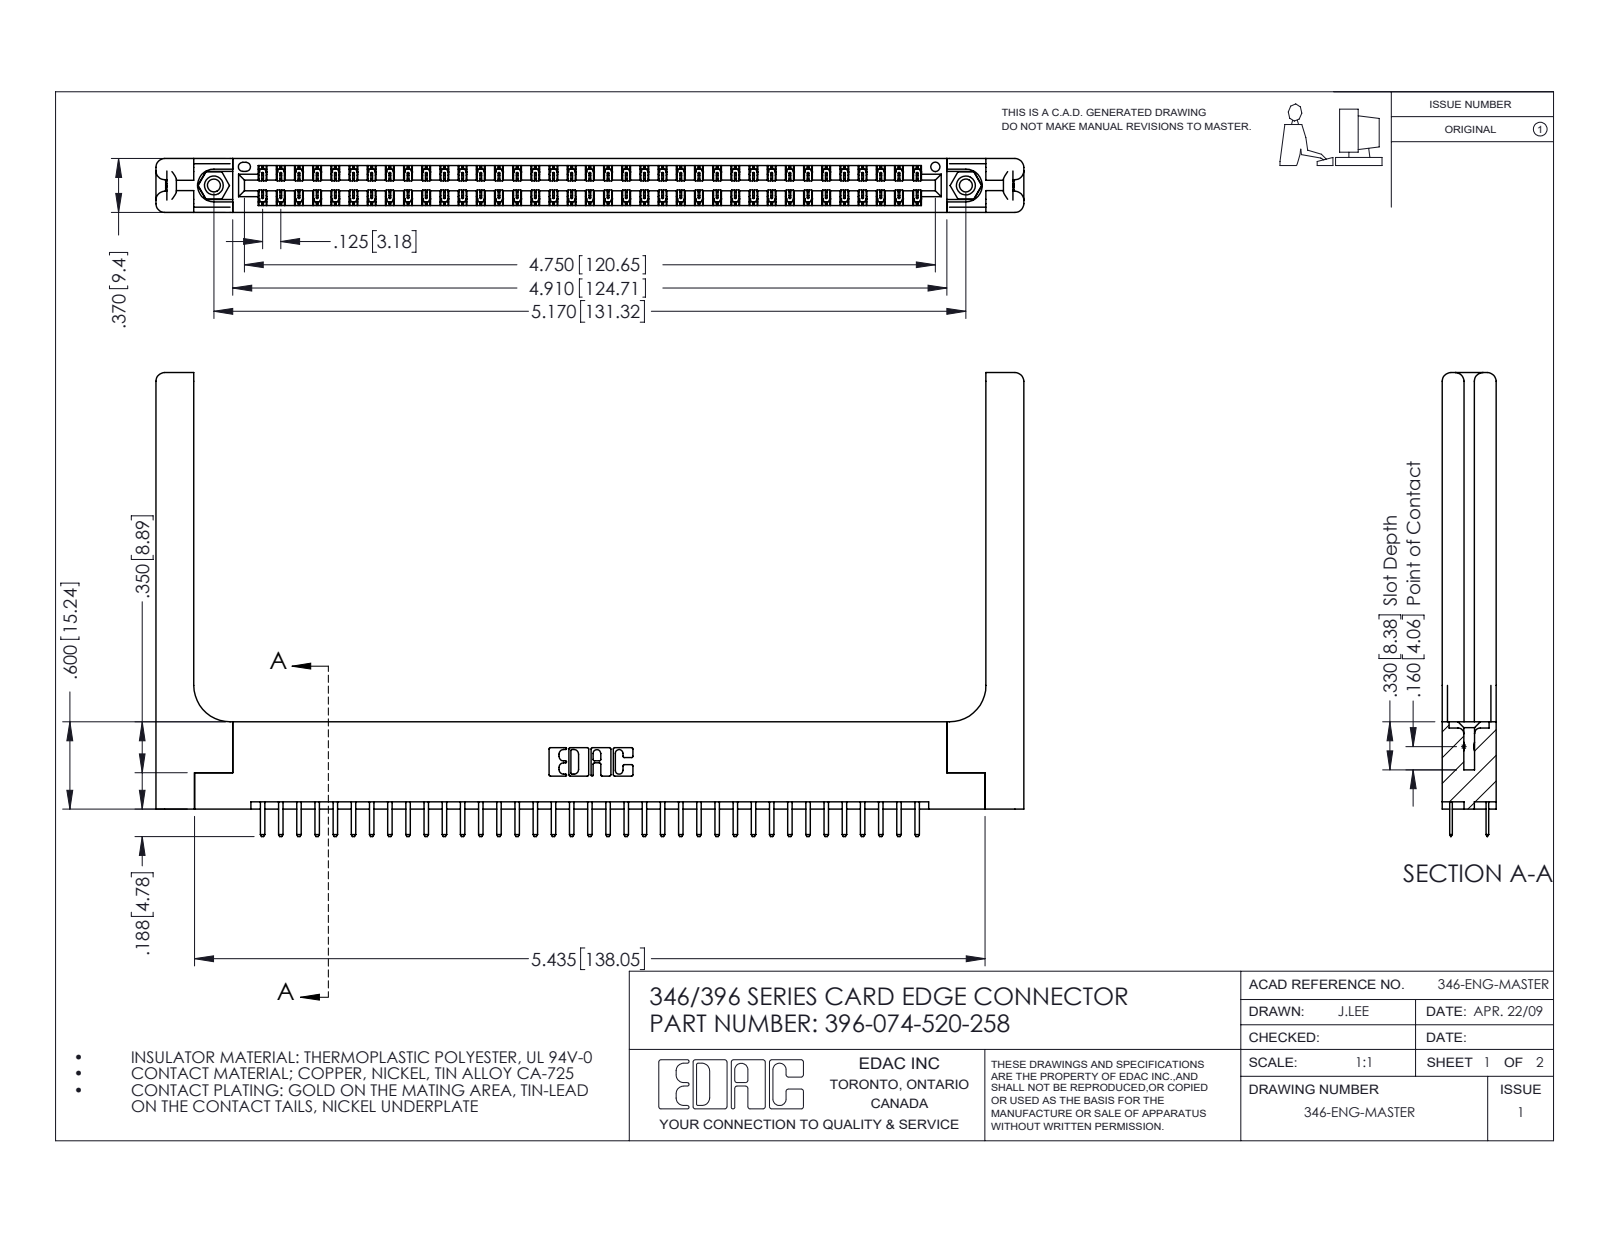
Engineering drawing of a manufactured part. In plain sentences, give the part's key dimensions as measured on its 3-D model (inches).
The part is named "345-250-001_345-250-001-102; 346 Part_Flush Mounting Lugs - 0.156 Dia-TH; 396-074-520-258; 346-220-058_345-220-058 (+1 more)". Its 3-D file was written by "SolidWorks 2016 (CONFIG_CONTROL_DESIGN)". It is 79 solids with 4522 faces: 2962 planar, 1500 cylindrical and 60 other. Overall it measures 5.966 by 3.188 by 0.37 inches. Its volume is 1.355 cubic inches and its surface area 38.8 square inches. Round holes: 2 of diameter 0.089, 2 of diameter 0.125, 2 of diameter 0.156, 1 of diameter 0.064. Round bosses or shafts: 2 of diameter 0.155. Partial cylindrical surfaces (rounded edges, fillets, slot ends): 111 of radius 0.006, 78 of radius 0.01, 22 of radius 0.01, 16 of radius 0.06, 6 of radius 0.007, 6 of radius 0.031, 3 of radius 0.026, 2 of radius 0.014. The main face-to-face distances are 0.37, 0.048, 0.322, 0.072, 0.25, 0.148, 0.15, 0.298, 0.025, 0.275. The hole center spacings are 0.246, 4.961, 5.17.
